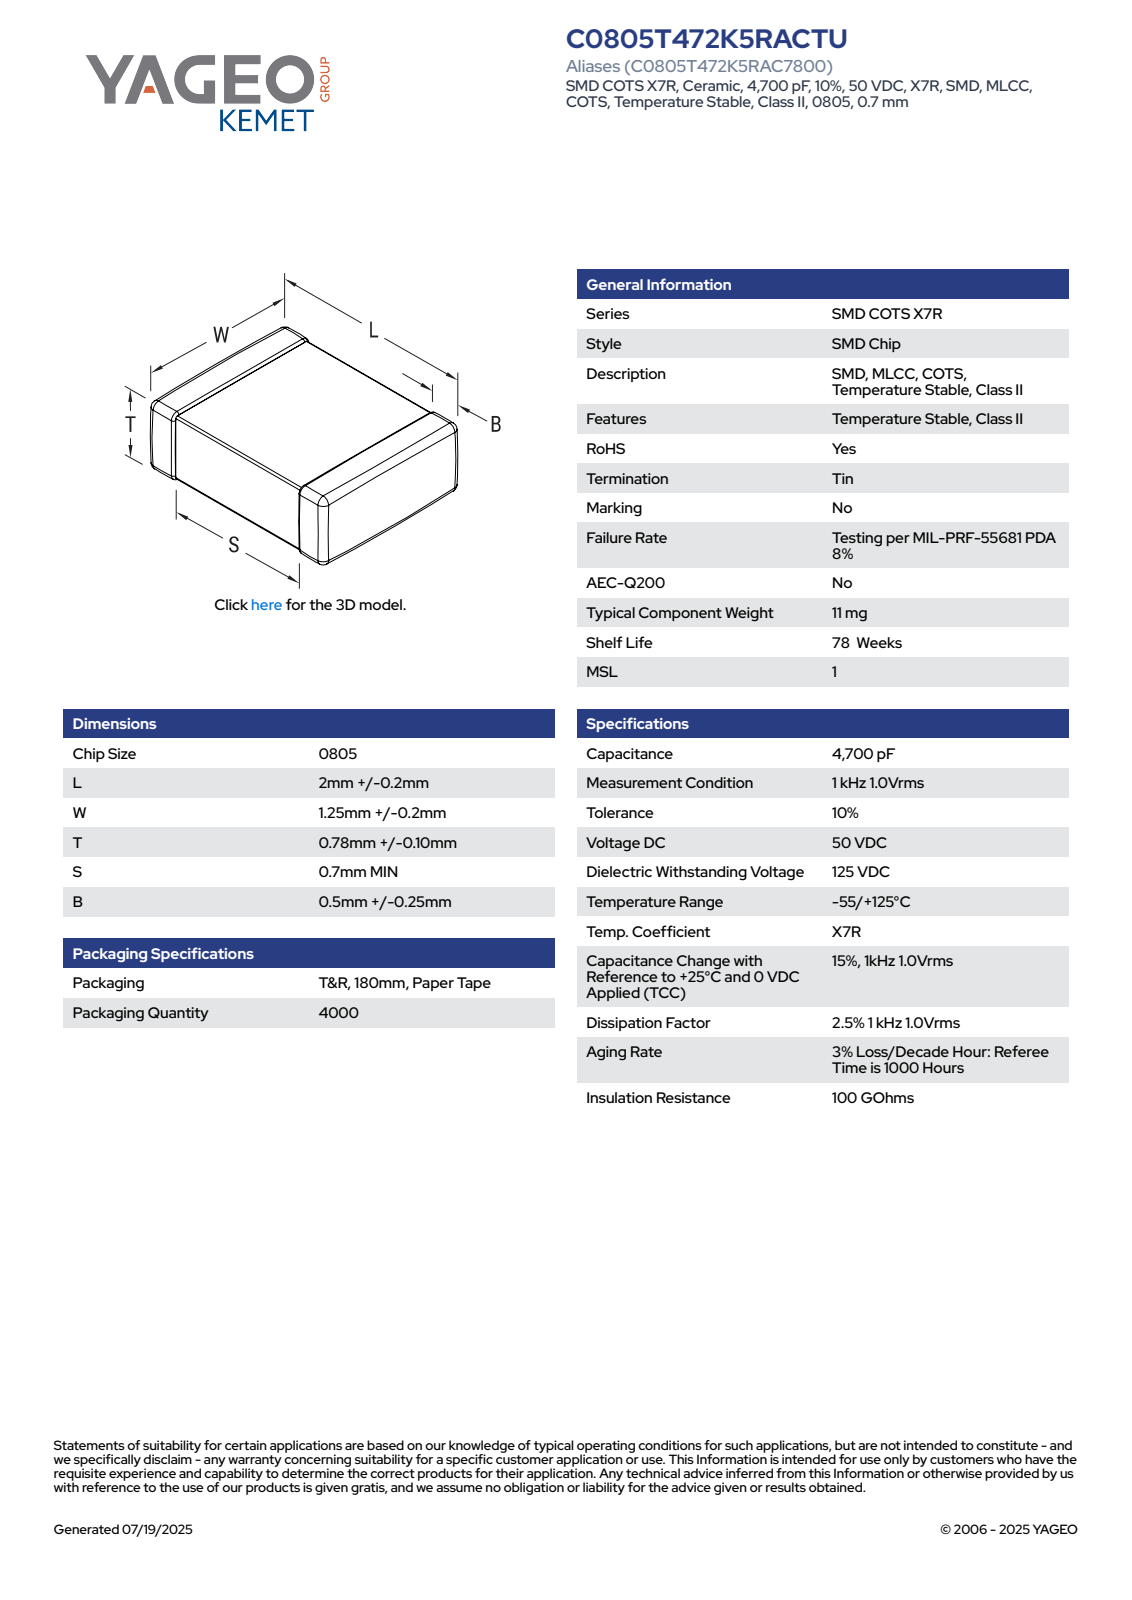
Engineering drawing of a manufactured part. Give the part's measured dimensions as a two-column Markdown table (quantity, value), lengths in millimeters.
| quantity | value |
| --- | --- |
| part name | CCSM_STD_0805_L2.2W1.45T0.88S0.78B0.75 |
| STEP written by | SolidWorks 2021 (AUTOMOTIVE_DESIGN) |
| units | millimeters |
| bodies | 4 solids, 121 faces (71 planar, 34 cylindrical, 16 other) |
| overall size | 2.2 × 1.45 × 0.88 |
| volume | 3 mm³ |
| surface area | 13 mm² |
| main face-to-face distances | 0.85, 0.88, 2.2, 1.45, 1.42, 0.82, 1.39, 0.97, 1.23, 1.19 |
